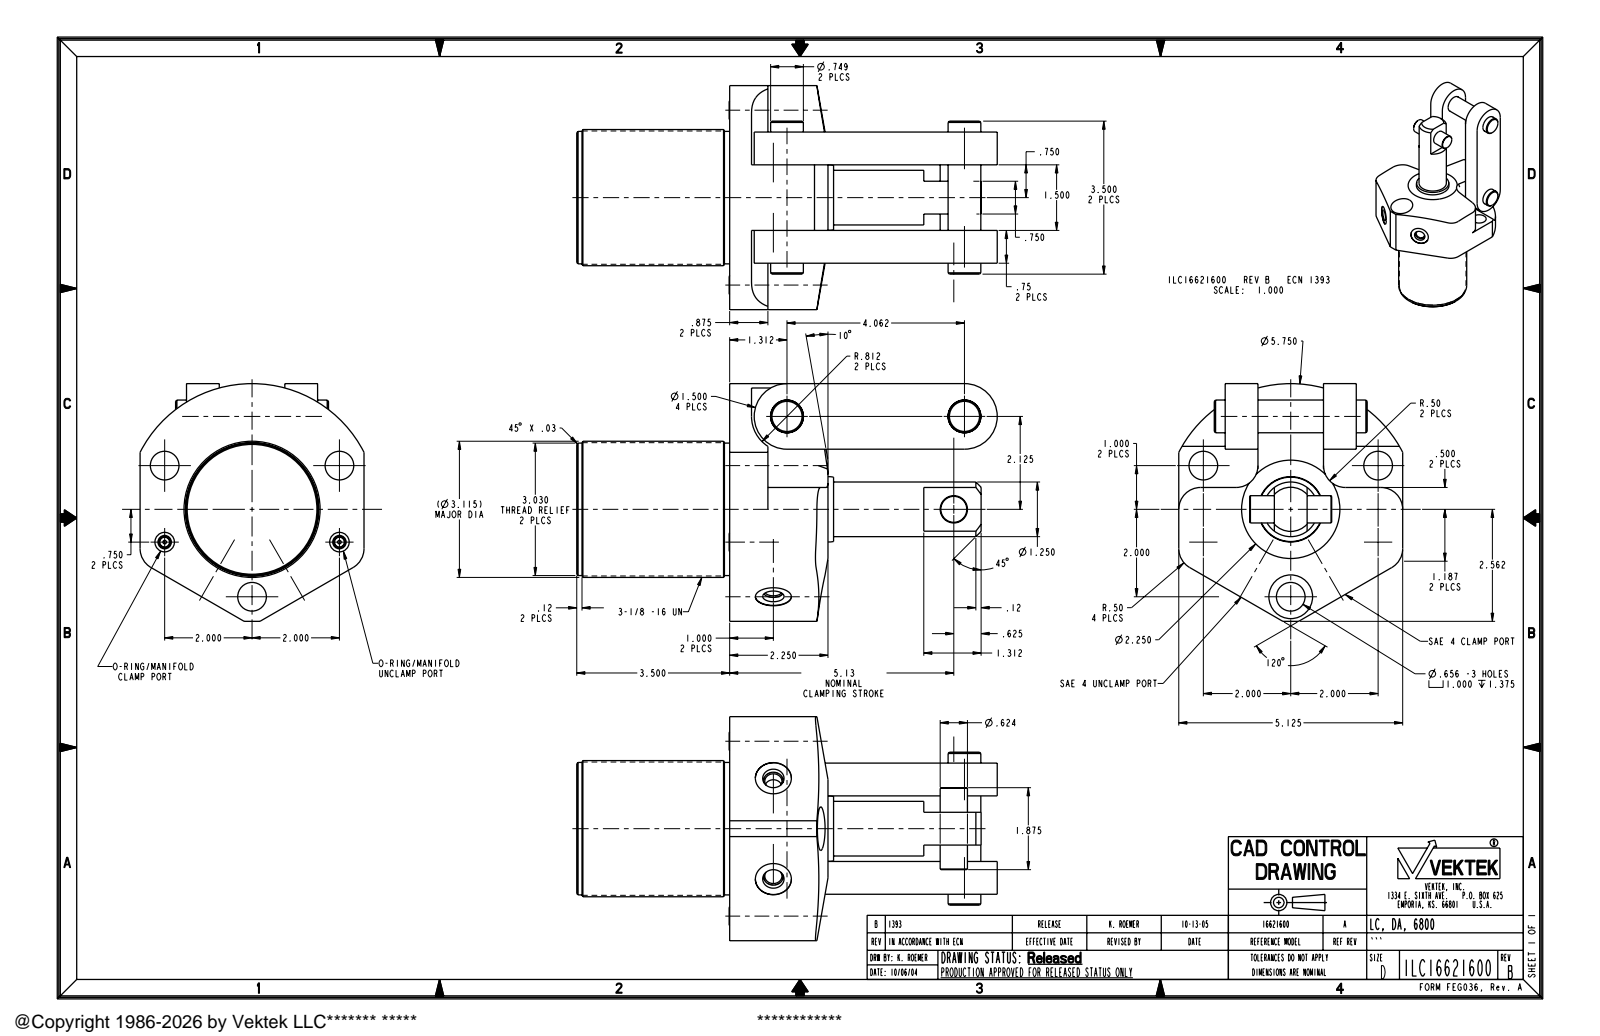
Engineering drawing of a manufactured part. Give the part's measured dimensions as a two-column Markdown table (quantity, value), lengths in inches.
| quantity | value |
| --- | --- |
| part name | ILC16621600 |
| STEP written by | PRO/ENGINEER BY PARAMETRIC TECHNOLOGY CORPORATION, 2004290 (AUTOMOTIVE_DESIGN_CC2) |
| units | inches |
| bodies | 1 solid, 300 faces (121 planar, 131 cylindrical, 48 other) |
| overall size | 9.624 × 5.438 × 5.125 |
| volume | 80.32 in³ |
| surface area | 224.7 in² |
| round holes (diameter × count) | 0.052 × 4, 0.656 × 3, 0.047 × 2, 0.098 × 2, 0.256 × 2, 0.392 × 2, 0.447 × 2, 0.825 × 2, 1 × 1 |
| round bosses / shafts (diameter × count) | 0.85 × 2, 0.75 × 2, 0.437 × 2, 0.224 × 2, 0.118 × 2, 3.115 × 1, 3.049 × 1, 3.03 × 1 |
| partial cylindrical surfaces (radius × count) | 0.052 × 8, 0.5 × 6, 0.047 × 4, 0.75 × 2, 0.812 × 1, 2.875 × 1 |
| main face-to-face distances | 2.25, 0.75, 3.5, 3, 1.5, 1.5, 1.063, 1.813, 3.313, 4.063 |
| hole center spacings | 0.125, 1.75, 2.359, 3.606, 4, 4.062, 4.064, 4.366 |
